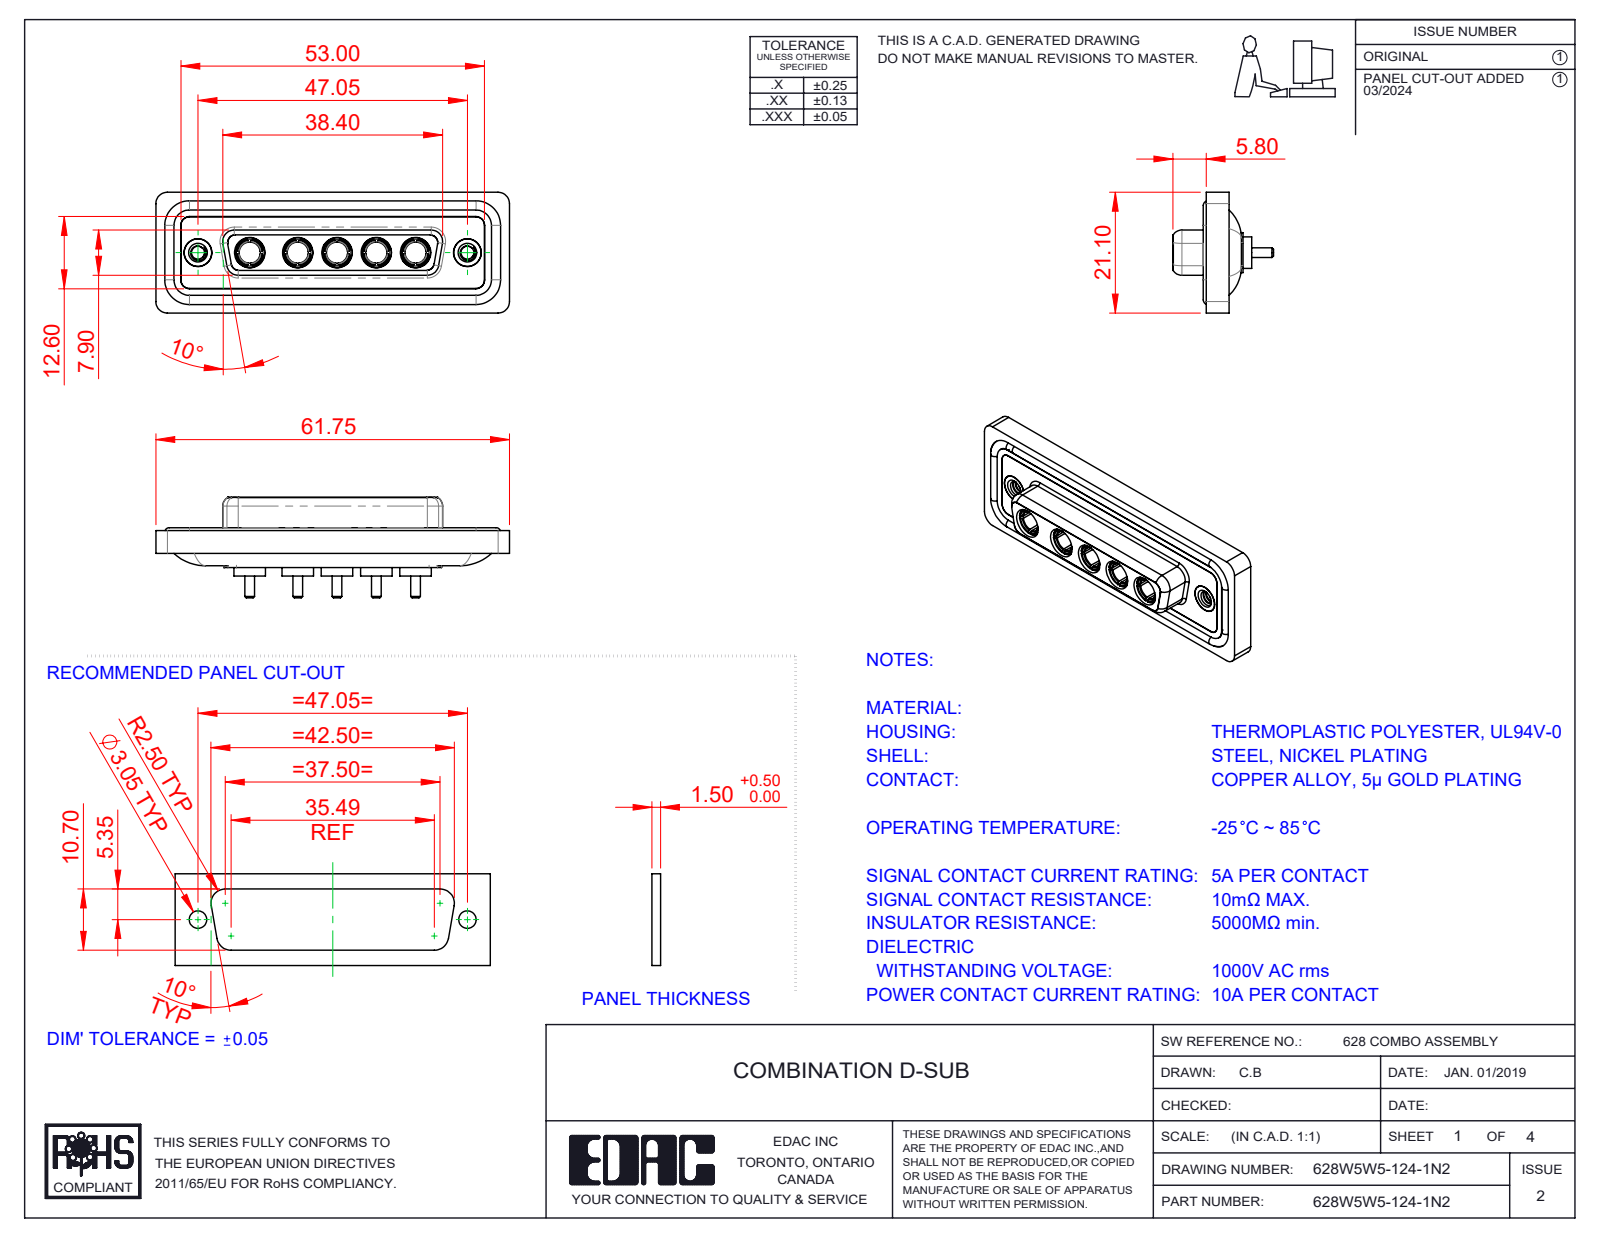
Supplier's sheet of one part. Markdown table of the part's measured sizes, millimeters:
| quantity | value |
| --- | --- |
| part name | 628Combo Shell Front_25 Contacts; 628Combo Shell Rear_25 Contacts; Power Socket_10A S; 628Combo Waterproof Housing_25 Contacts (+3 more) |
| STEP written by | SolidWorks 2023 (CONFIG_CONTROL_DESIGN) |
| units | millimeters |
| bodies | 17 solids, 756 faces (250 planar, 303 cylindrical, 203 other) |
| overall size | 61.75 × 21.1 × 17.55 |
| volume | 8 099 mm³ |
| surface area | 13 352 mm² |
| round holes (diameter × count) | 4.85 × 7, 3.7 × 5, 5.3 × 5, 2.26 × 2, 4 × 2, 4.05 × 2, 5 × 2 |
| round bosses / shafts (diameter × count) | 5.5 × 5, 5.2 × 5, 4.96 × 5, 4.75 × 5, 3.75 × 5, 1.7 × 5, 1.6 × 4, 4.95 × 2 |
| partial cylindrical surfaces (radius × count) | 1.5 × 22, 2 × 18, 1.35 × 8, 1.6 × 8, 2.1 × 5, 0.25 × 4, 0.5 × 4, 0.6 × 4 |
| main face-to-face distances | 0.4, 1.8, 7.45, 5.65, 0.5, 7.05, 6.6, 1.6, 1.1, 1.5 |
| hole center spacings | 6.86, 9.04, 13.72, 38.01, 8.39, 15.25, 15.9, 17.43 |
